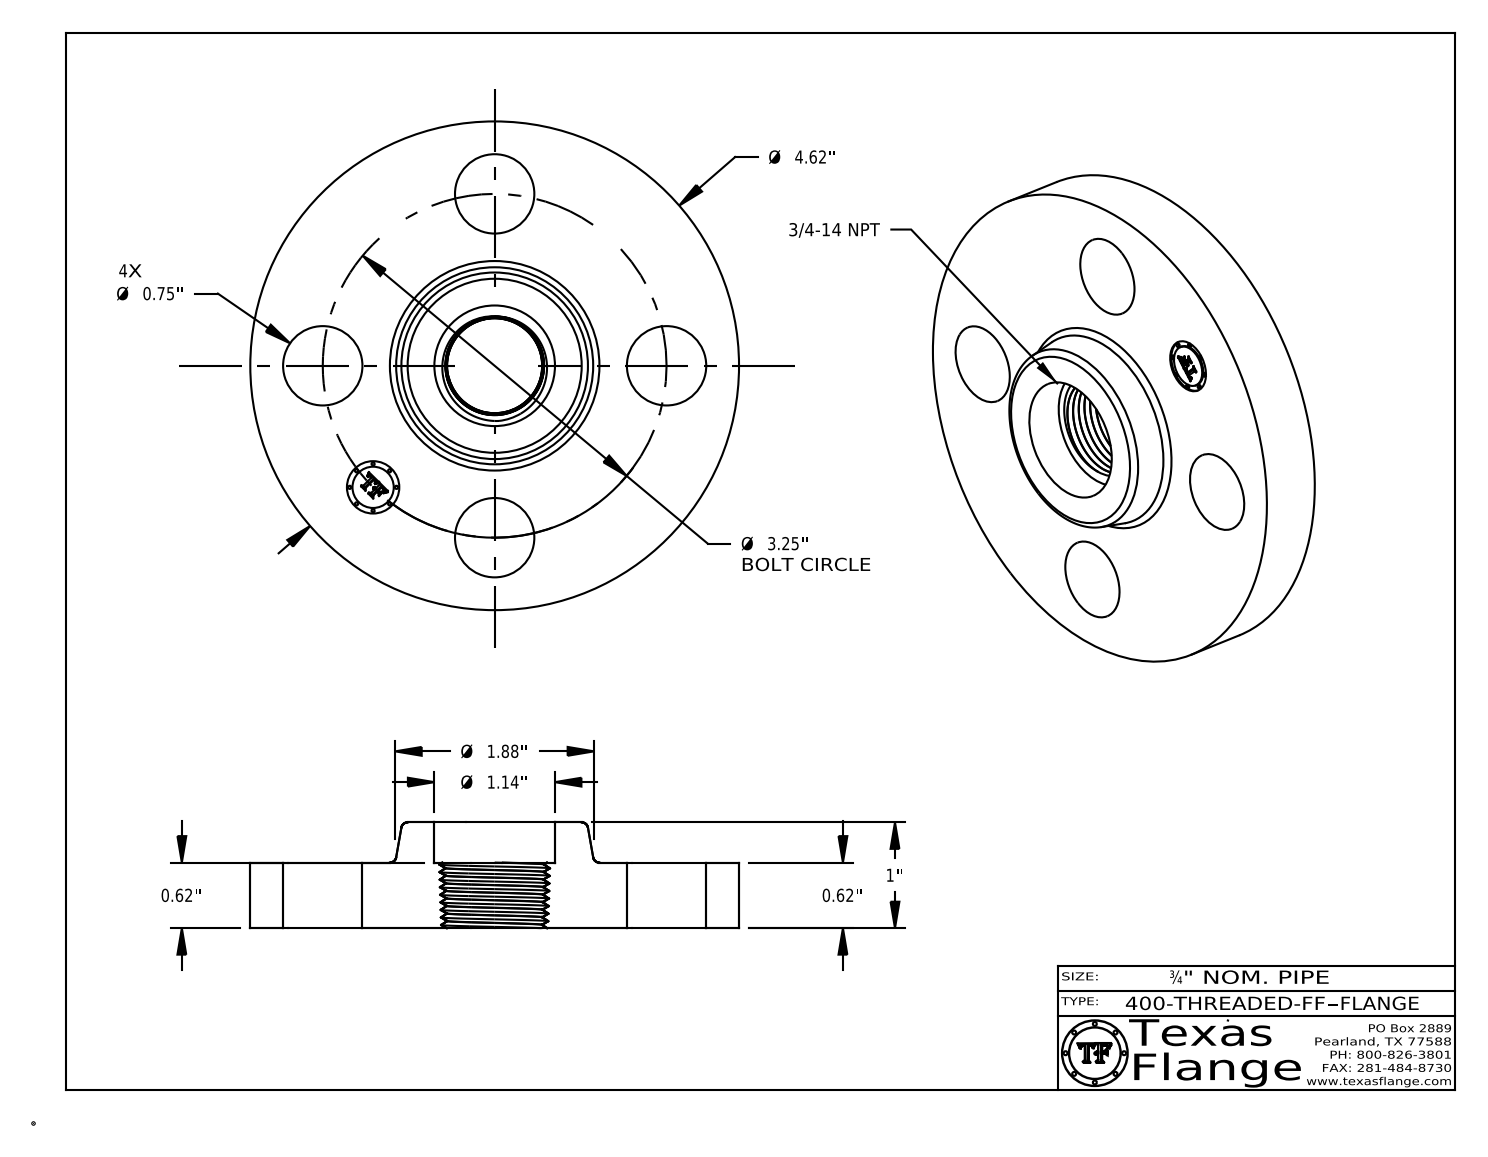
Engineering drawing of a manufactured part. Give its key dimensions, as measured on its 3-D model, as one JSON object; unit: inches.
{"part_name": "400-THREADED-FF", "step_written_by": "CATIA V5 STEP AP214 (AUTOMOTIVE_DESIGN)", "units": "inches", "bodies": {"solids": 1, "faces": 500, "planar": 369, "cylindrical": 32, "other": 99}, "overall_size": [4.62, 4.62, 1], "volume_in3": 9.432, "surface_area_in2": 49.96, "round_holes": [[0.75, 4], [0.495, 1], [1.14, 1]], "round_bosses_or_shafts": [[0.03, 8], [4.62, 1], [0.39, 1]], "face_to_face_distances": [0.62, 1, 0.38, 0.605, 0.015, 0.395, 0.148, 0.144, 0.027, 0.096], "hole_center_spacings": [1.625, 2.298, 1.244, 3.003, 3.25]}
